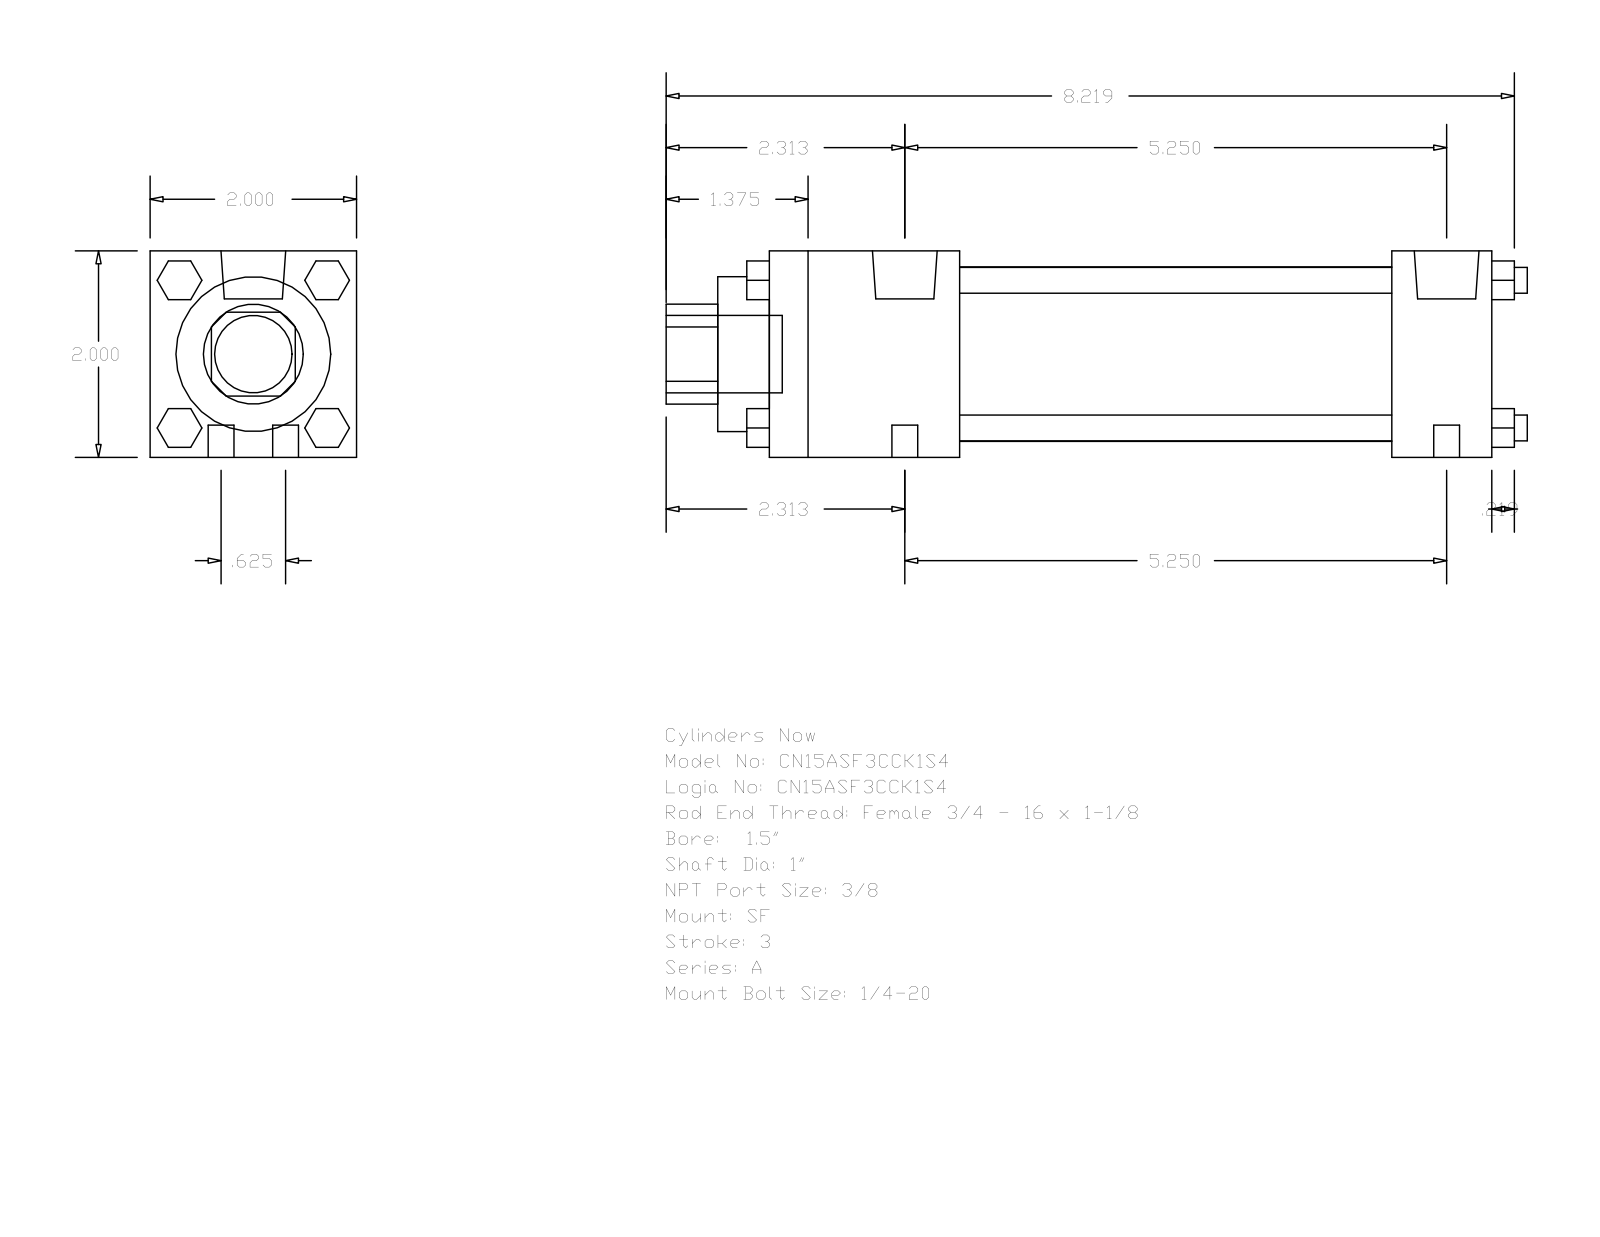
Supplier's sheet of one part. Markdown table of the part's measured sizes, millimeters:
| quantity | value |
| --- | --- |
| part name | A_SF__0150_1 |
| STEP written by | GSSL Pune (CONFIG_CONTROL_DESIGN) |
| units | millimeters |
| bodies | 0 solids, 124 faces (94 planar, 30 cylindrical, 0 other) |
| overall size | 211.93 × 50.8 × 50.8 |
| round holes (diameter × count) | 25.4 × 1, 38.1 × 1, 42.93 × 1 |
| round bosses / shafts (diameter × count) | 6.35 × 8, 15.93 × 2, 5.56 × 2, 19.05 × 1 |
| partial cylindrical surfaces (radius × count) | 12.29 × 1 |
| main face-to-face distances | 50.8, 177.8, 46.83, 153.19, 106.36, 130.97, 24.61, 12.7, 59.53, 165.89 |
